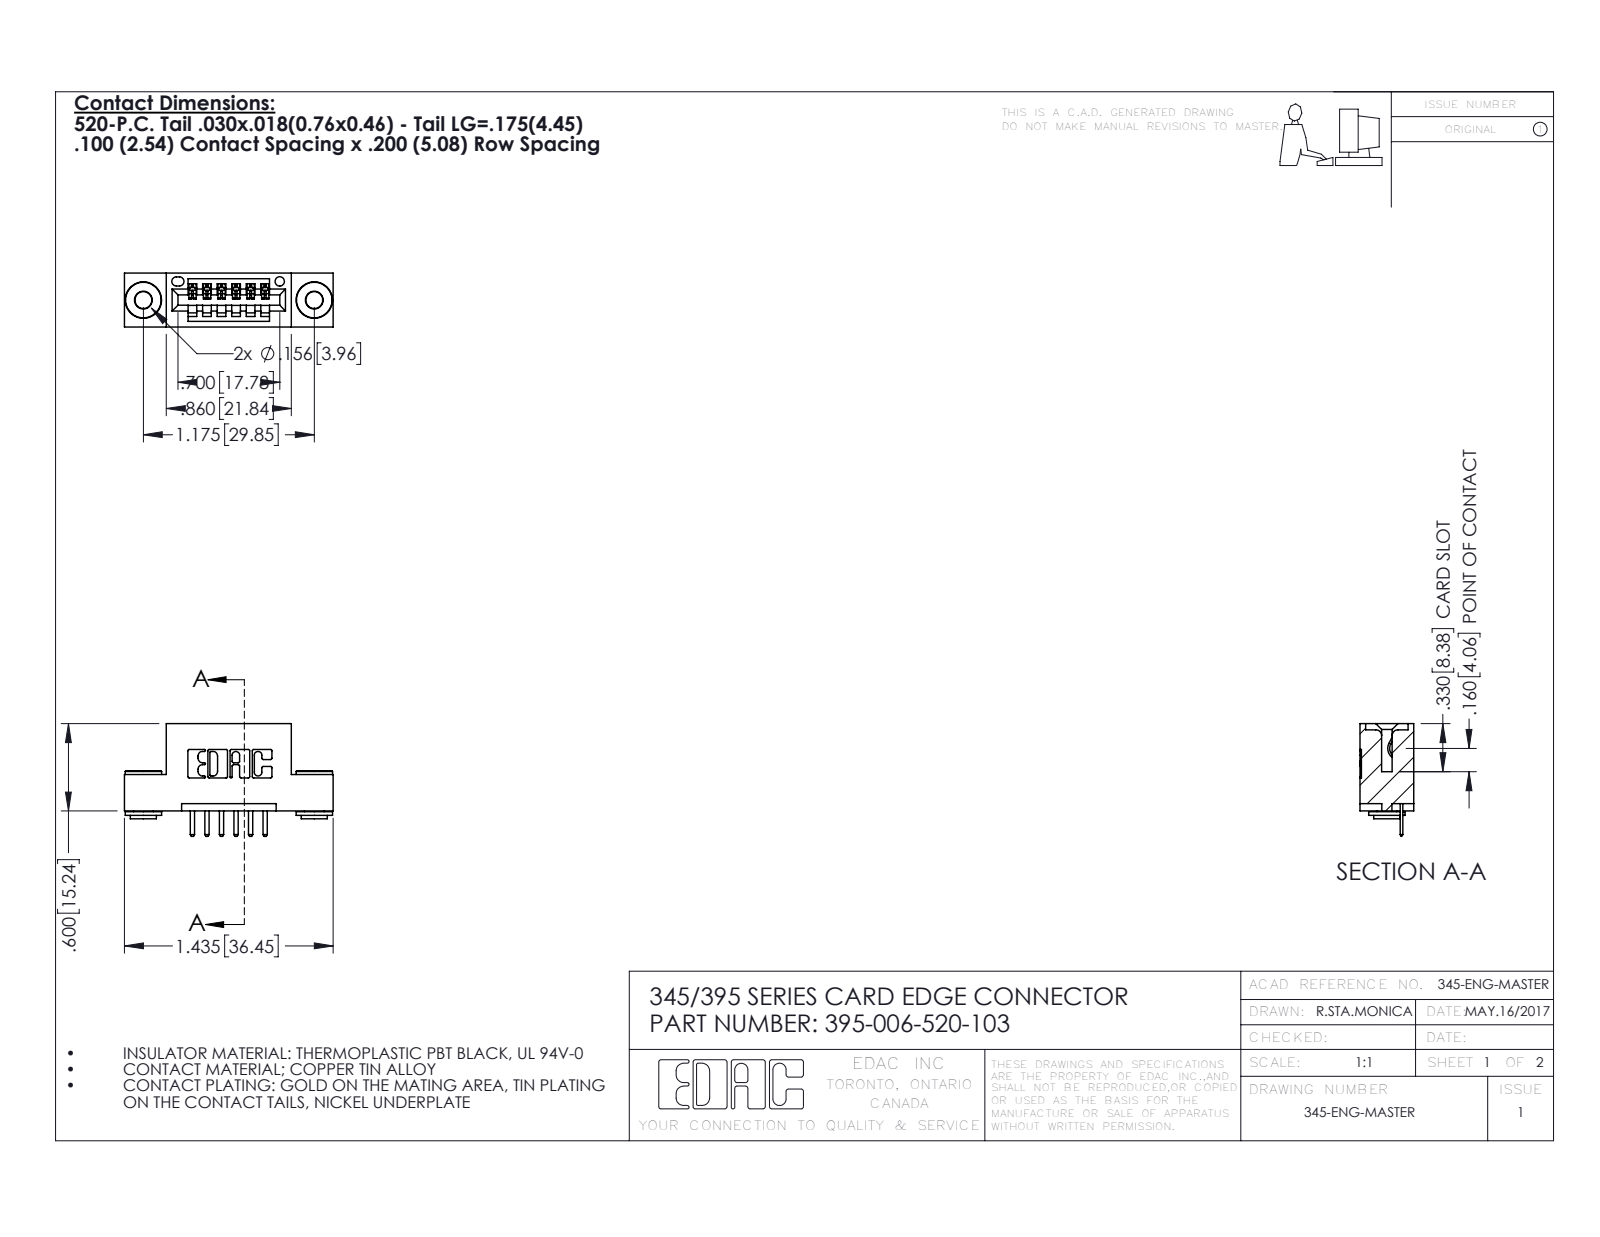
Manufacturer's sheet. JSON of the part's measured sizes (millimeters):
{"part_name": "345 Part_Flush Mounting Lugs - 0.156 Dia-TH; 395-006-520-103; 345-250-002_345-250-002-102; 345-292-001_345-293-120", "step_written_by": "SolidWorks 2016 (CONFIG_CONTROL_DESIGN)", "units": "millimeters", "bodies": {"solids": 9, "faces": 536, "planar": 342, "cylindrical": 186, "other": 8}, "overall_size": [36.4, 19.7, 9.4], "volume_mm3": 3160, "surface_area_mm2": 3881, "round_holes": [[2.9, 2], [4, 2], [1.6, 1]], "round_bosses_or_shafts": [[6.4, 2], [4.6, 2], [3.5, 2]], "partial_cylinders_radius": [[0.3, 22], [0.3, 14], [0.2, 12], [0.2, 6], [0.8, 6], [0.7, 3], [0.8, 2], [1, 2]], "face_to_face_distances": [5.1, 9.4, 2.5, 1.8, 7.6, 6.4, 0.6, 7.6, 1.5, 5.7], "hole_center_spacings": [6.9, 24, 29.8]}
